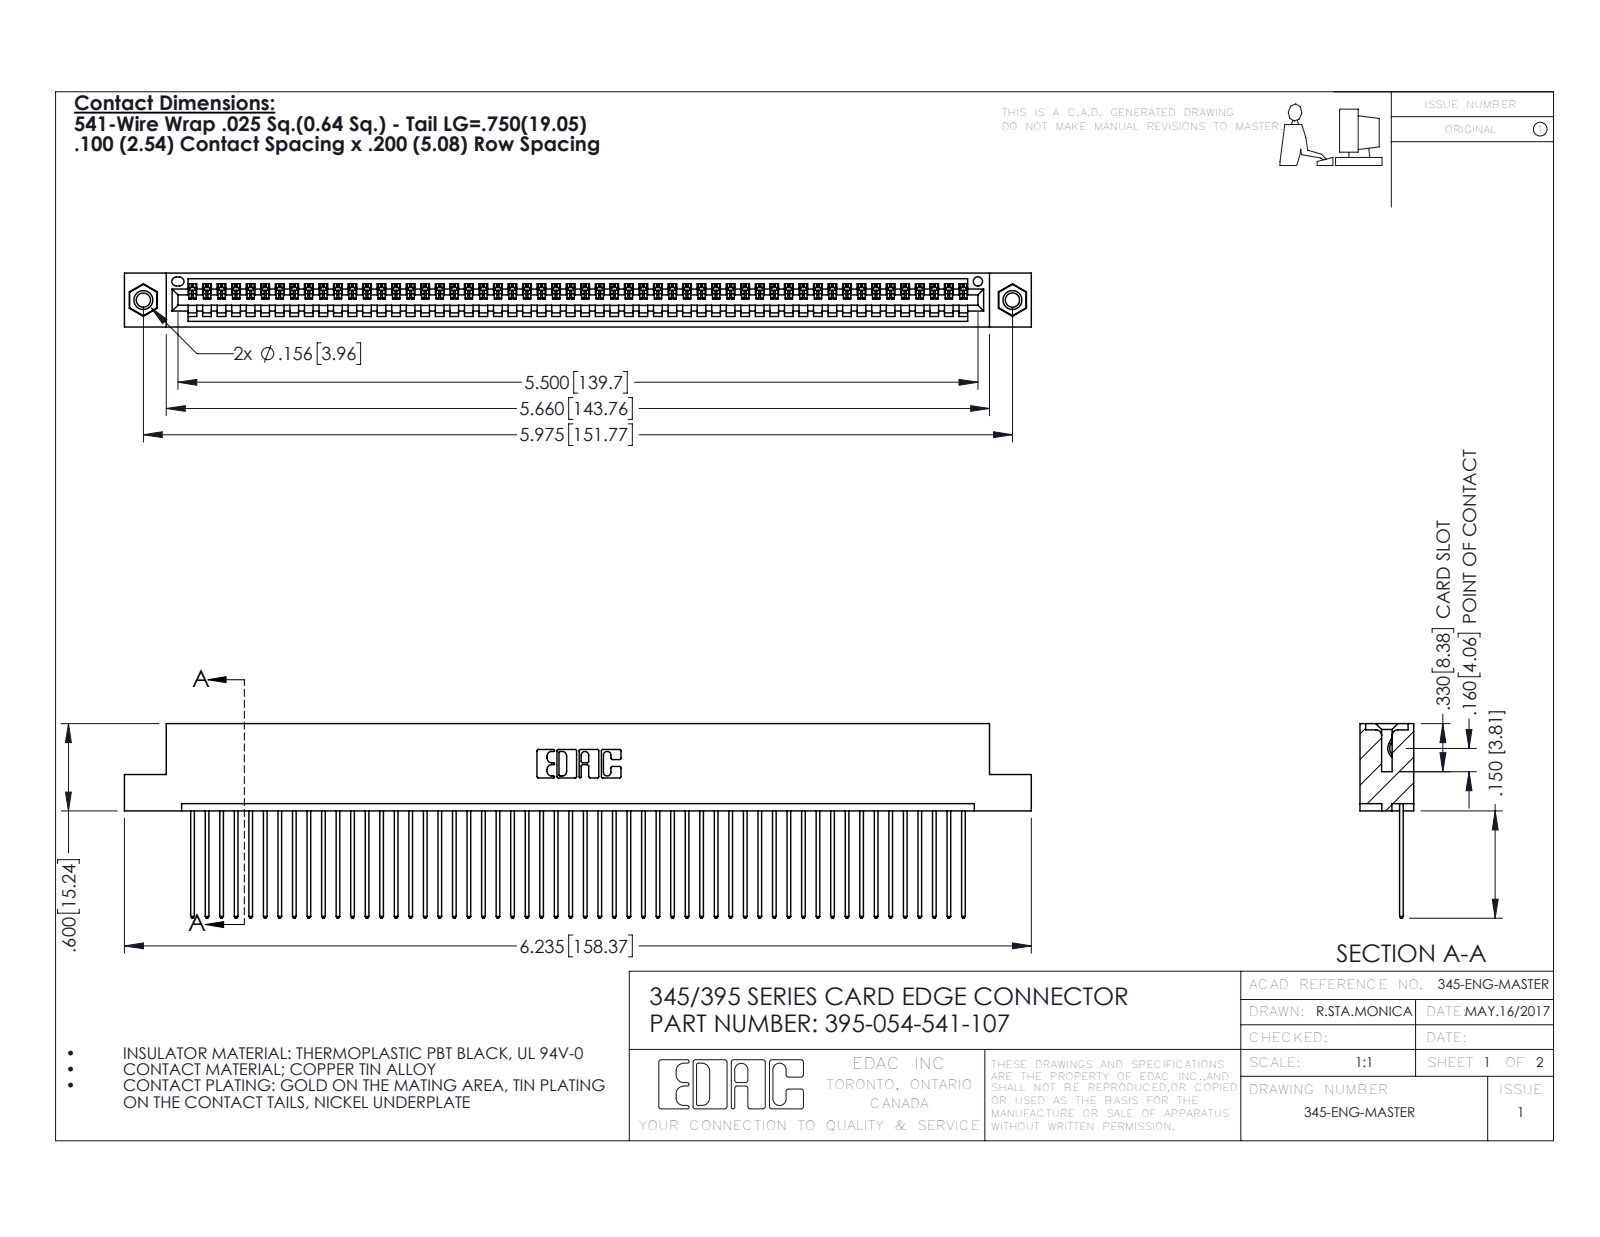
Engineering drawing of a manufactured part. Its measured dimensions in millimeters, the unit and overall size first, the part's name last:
Units: millimetres
Overall size (bounding box): 158.4 × 34 × 9.4
Round holes (diameter × count): ⌀2.5 ×2, ⌀3.2 ×2, ⌀4 ×2, ⌀1.6 ×1
Round bosses / shafts (diameter × count): ⌀3.9 ×2
Partial cylindrical surfaces — rounded edges, fillets, slot ends (radius × count): R0.2 ×108, R0.3 ×108, R0.3 ×22, R0.2 ×6, R0.8 ×6, R0.7 ×3, R0.8 ×2, R1 ×2
Main face-to-face distances: 1.8, 7.6, 2.5, 6.9, 0.6, 9.4, 5.1, 5.7, 3.8, 1.8
Hole centre spacings: 6.9, 145.8, 151.8
Volume: 15 300 mm³ · Surface area: 21 580 mm²
Bodies: 57 solids, 3318 faces (2272 planar, 1030 cylindrical, 16 other)
Part name (STEP PRODUCT): 345 Part_Flush Mounting Lugs - 0.156 Dia-TI; 345-250-001_345-250-005-103; 395-054-541-107; 345-292-001_345-293-141
STEP written by: SolidWorks 2016 (CONFIG_CONTROL_DESIGN)
